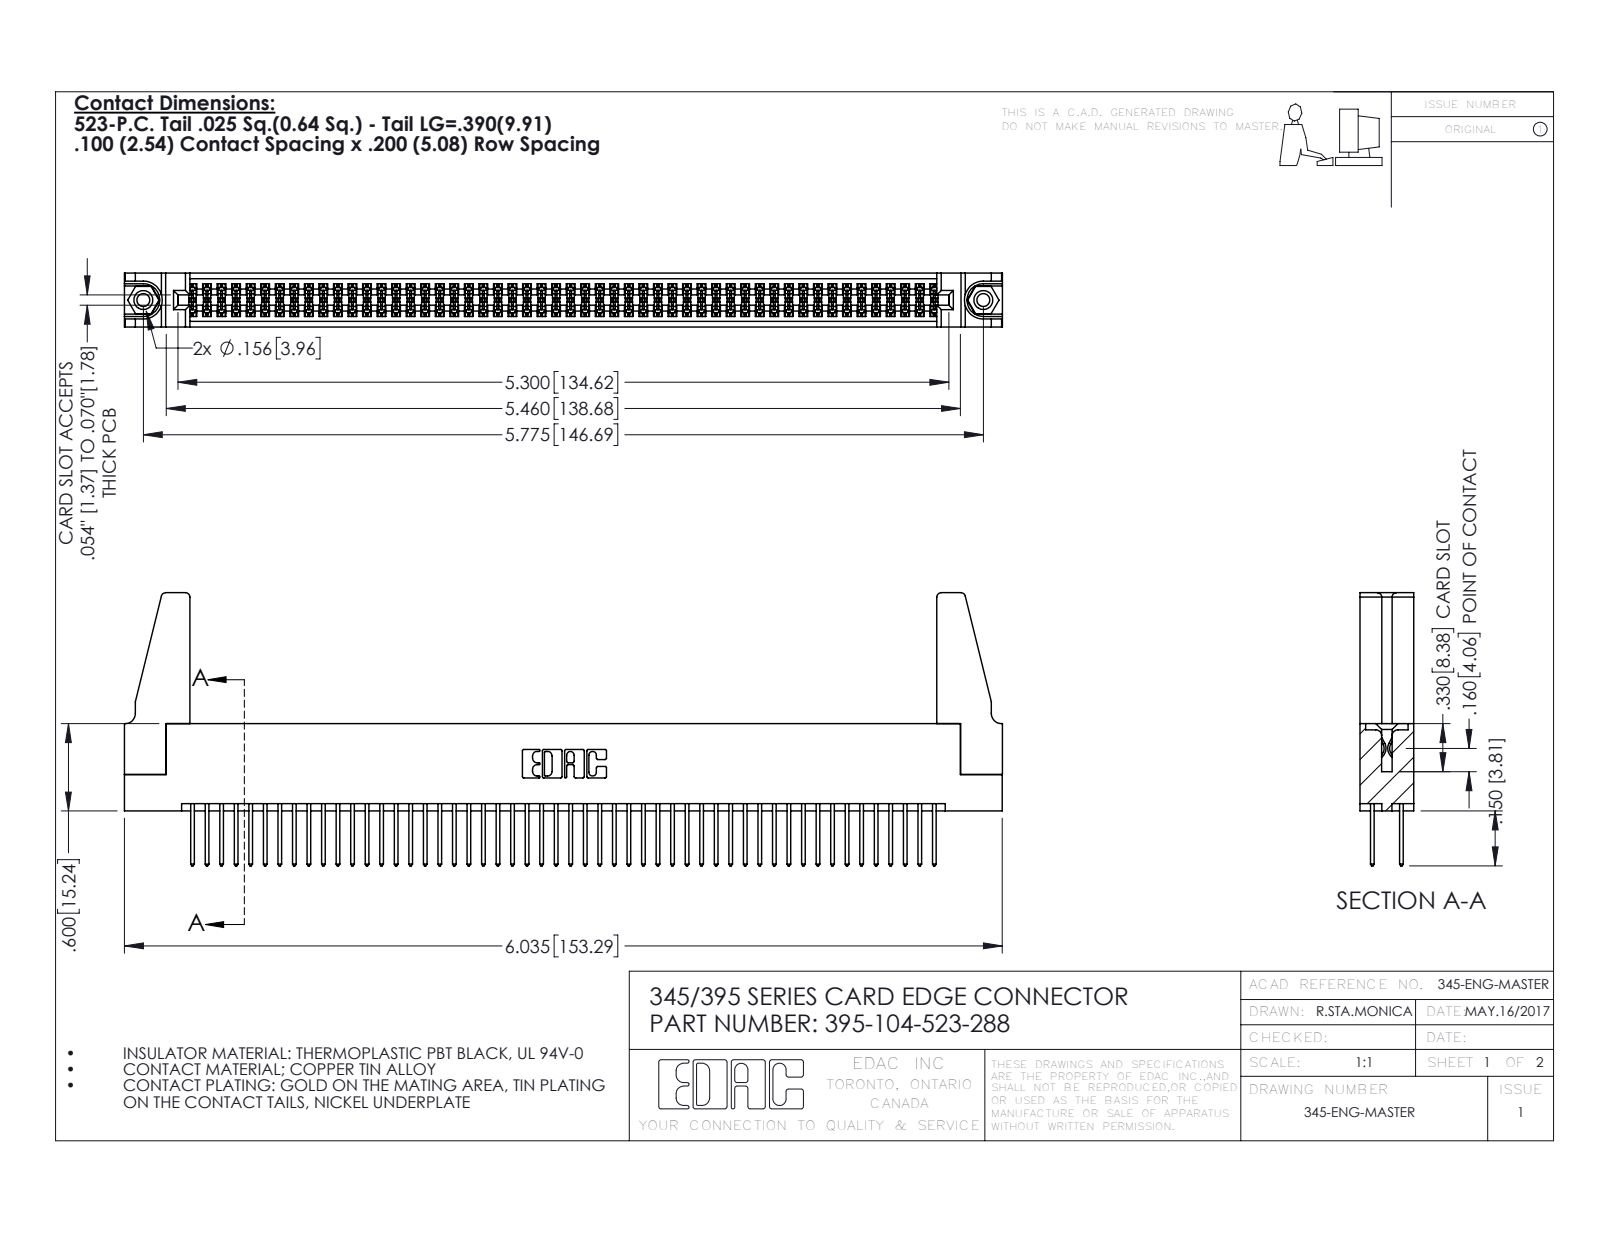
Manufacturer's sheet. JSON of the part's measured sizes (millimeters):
{"part_name": "345-250-001_345-250-001-102; 345 Part_Flush Mounting Lugs - 0.156 Dia-TH; 395-104-523-288; 345-292-001_345-293-123 (+1 more)", "step_written_by": "SolidWorks 2016 (CONFIG_CONTROL_DESIGN)", "units": "millimeters", "bodies": {"solids": 109, "faces": 5450, "planar": 3584, "cylindrical": 1850, "other": 16}, "overall_size": [153.3, 47.7, 9.4], "volume_mm3": 18450, "surface_area_mm2": 26740, "round_holes": [[2.3, 2], [3.2, 2], [4, 2], [1.6, 1]], "round_bosses_or_shafts": [[3.9, 2]], "partial_cylinders_radius": [[0.2, 156], [0.3, 104], [0.3, 22], [0.8, 8], [0.2, 6], [0.8, 6], [0.7, 3], [0.4, 2]], "face_to_face_distances": [1.8, 7.6, 5.1, 9.4, 2.5, 6.9, 0.6, 5.7, 4.4, 3.8], "hole_center_spacings": [6.9, 140.7, 146.7]}
